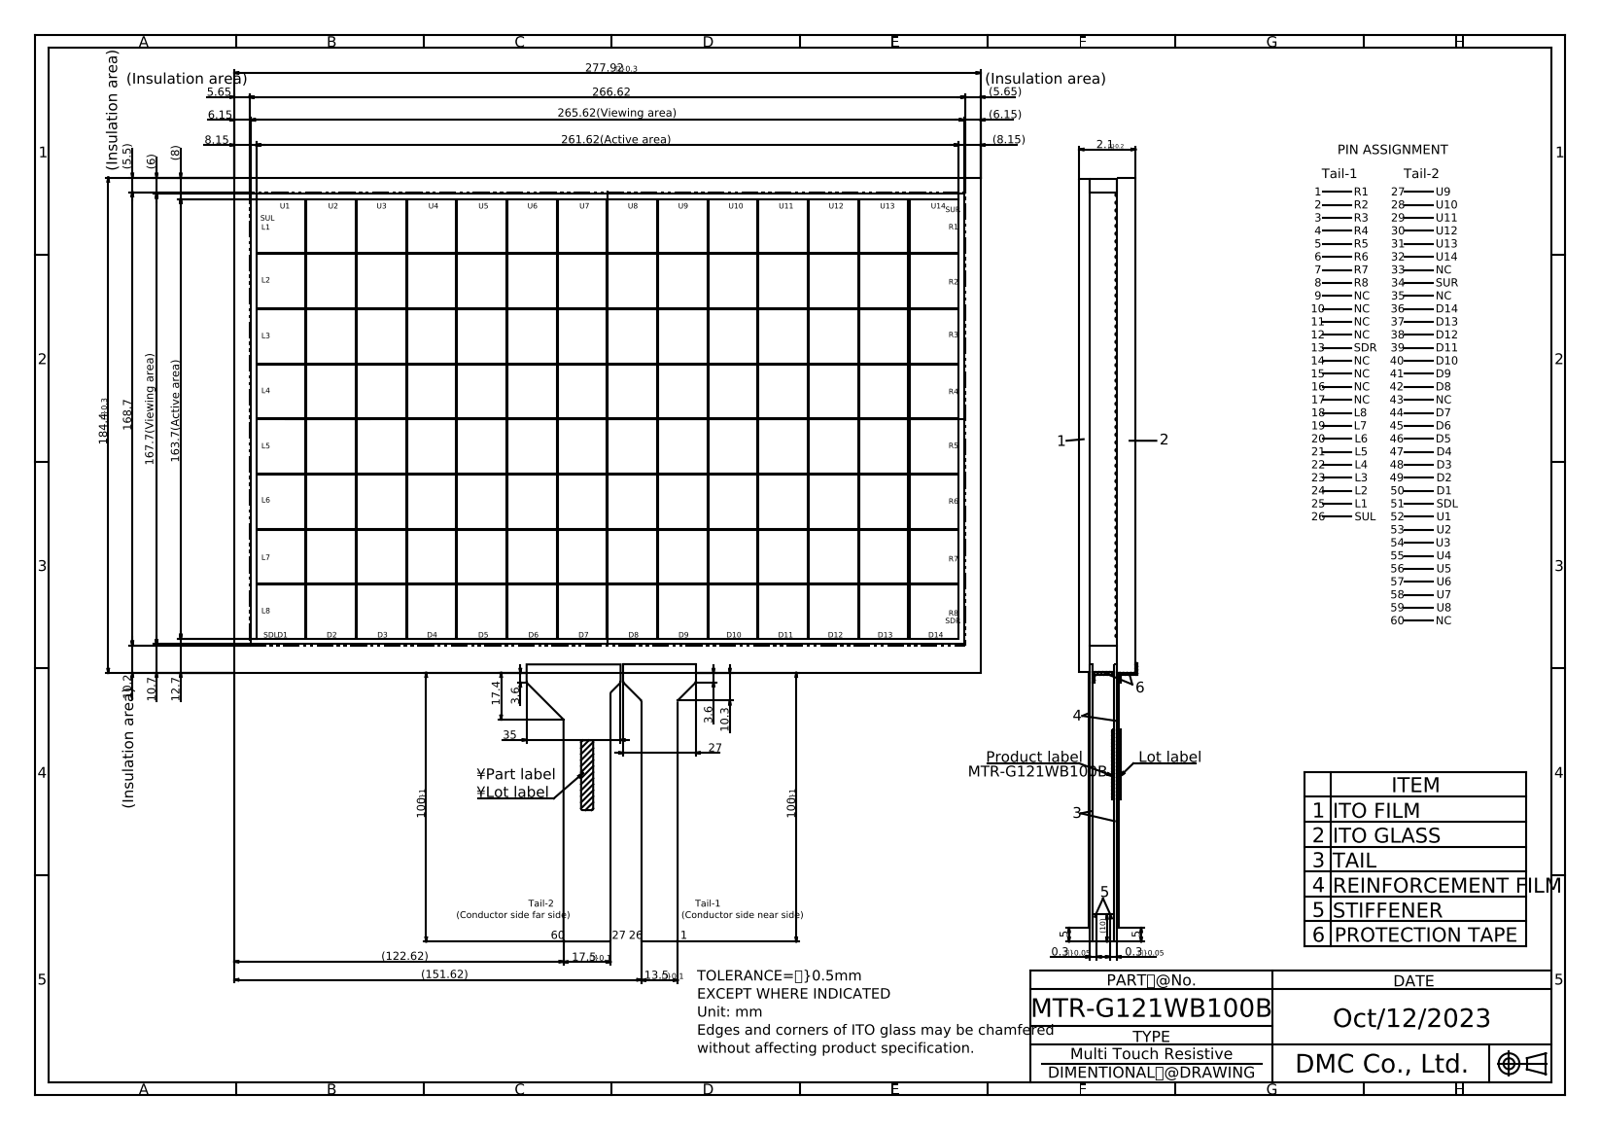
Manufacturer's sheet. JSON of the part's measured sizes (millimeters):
{"part_name": "MTR-G121WB100B", "step_written_by": "Autodesk Inventor 2020 (CONFIG_CONTROL_DESIGN)", "units": "millimeters", "bodies": {"solids": 1, "faces": 294, "planar": 282, "cylindrical": 12, "other": 0}, "overall_size": [389.09, 321.28, 2.2], "volume_mm3": 107863, "surface_area_mm2": 111401, "partial_cylinders_radius": [[1, 8], [0.2, 4]], "face_to_face_distances": [2.1, 1.8, 1.9, 2, 184.4, 277.92, 0.4, 2.2, 0.5, 0.7]}
